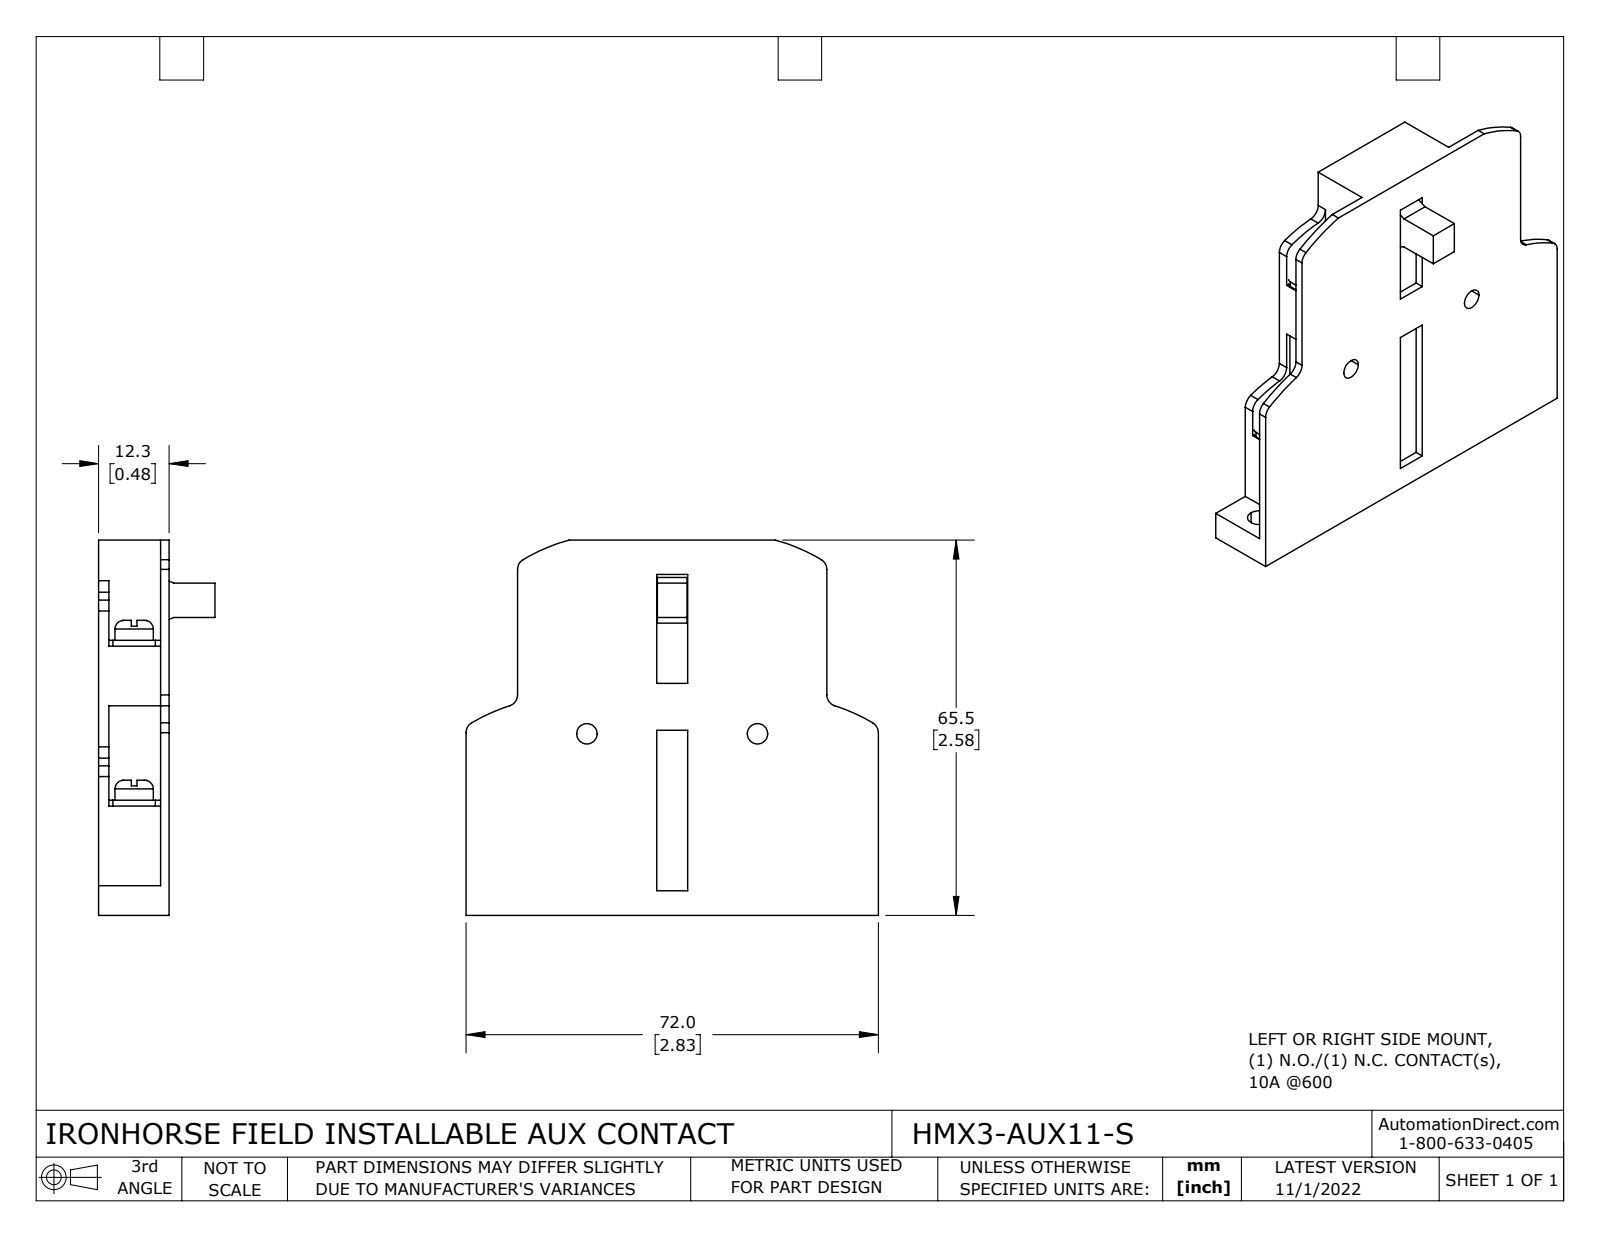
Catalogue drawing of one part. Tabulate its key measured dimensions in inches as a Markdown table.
| quantity | value |
| --- | --- |
| part name | HMX3-AUX11-S |
| STEP written by | SolidWorks 2021 (CONFIG_CONTROL_DESIGN) |
| units | inches |
| bodies | 5 solids, 211 faces (137 planar, 50 cylindrical, 24 other) |
| overall size | 2.835 × 2.579 × 0.799 |
| volume | 2.189 in³ |
| surface area | 22.06 in² |
| round holes (diameter × count) | 0.14 × 2, 0.165 × 2, 0.315 × 2 |
| round bosses / shafts (diameter × count) | 0.264 × 4 |
| partial cylindrical surfaces (radius × count) | 0.079 × 14, 0.039 × 8, 0.984 × 4, 1.26 × 4 |
| main face-to-face distances | 0.484, 0.059, 0.425, 1.098, 0.354, 0.039, 0.031, 0.413, 0.071, 1.551 |
| hole center spacings | 1.173, 2.48 |
